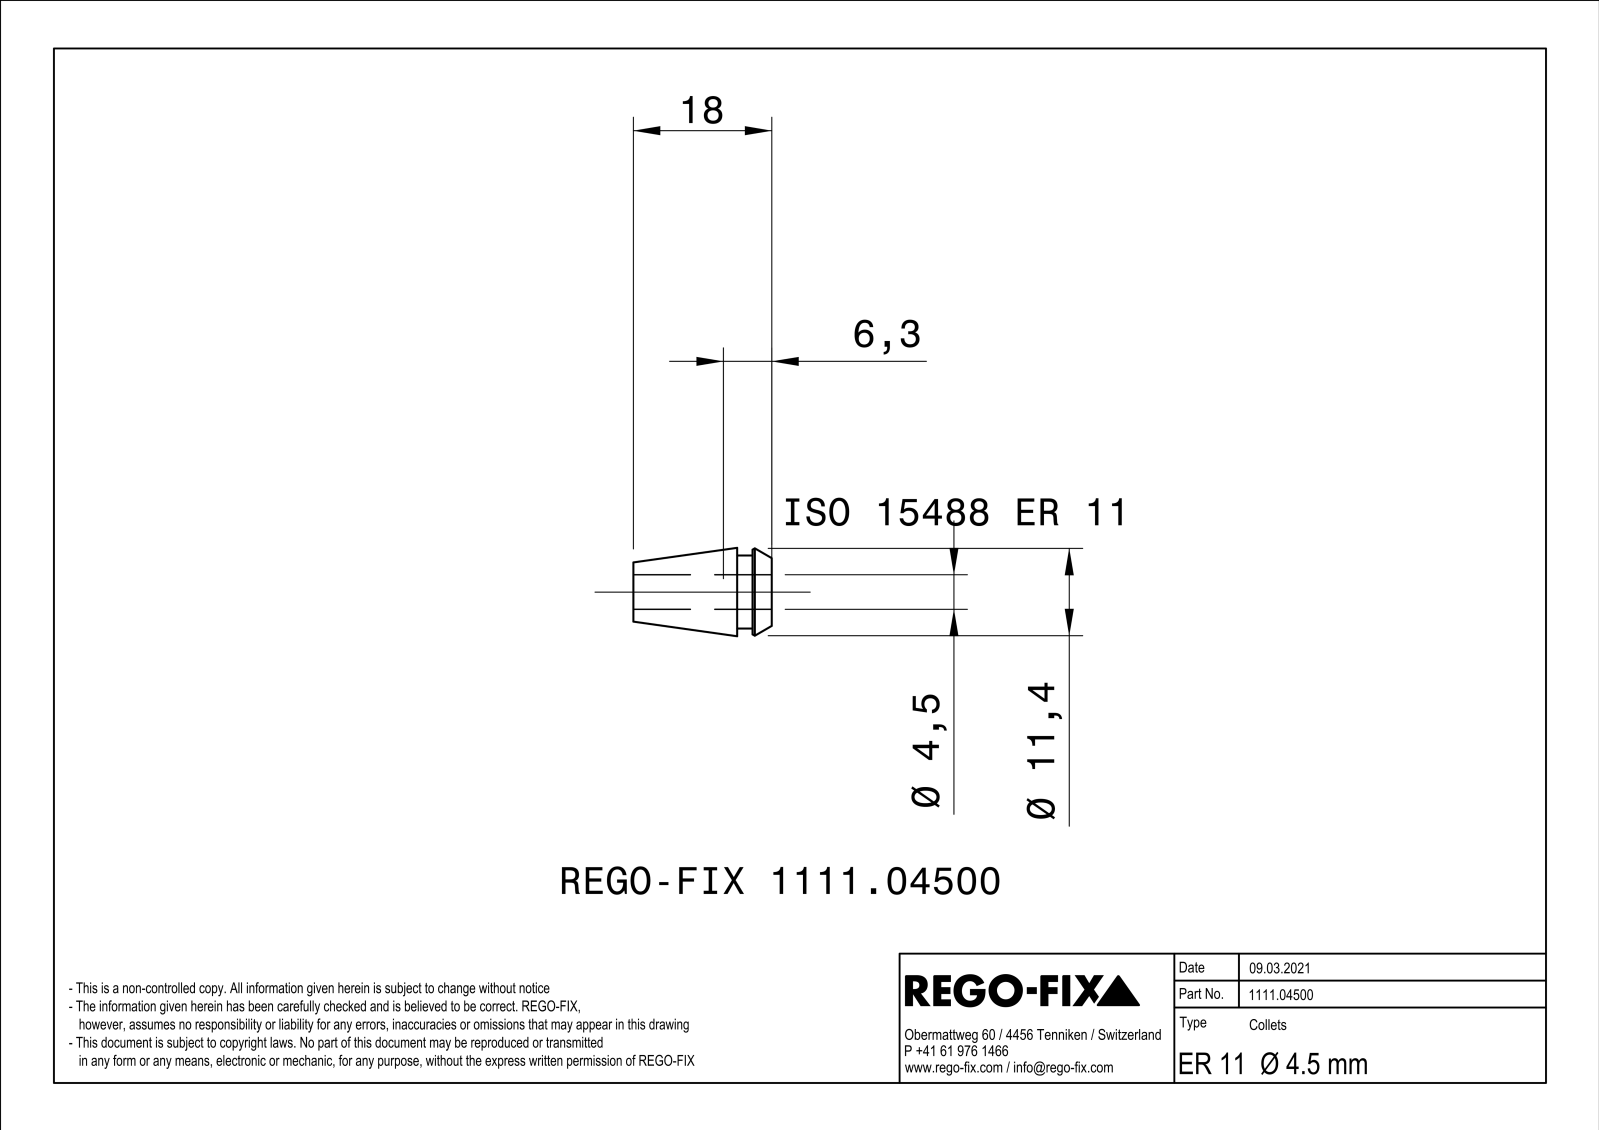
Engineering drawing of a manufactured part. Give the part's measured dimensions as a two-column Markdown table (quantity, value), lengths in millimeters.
| quantity | value |
| --- | --- |
| part name | NOCUT |
| STEP written by | SIEMENS PLM Software Solid Edge ST10 (AUTOMOTIVE_DESIGN) |
| units | millimeters |
| bodies | 1 solid, 157 faces (66 planar, 37 cylindrical, 54 other) |
| overall size | 18 × 11.5 × 11.49 |
| volume | 850 mm³ |
| surface area | 1 693 mm² |
| round holes (diameter × count) | 4.5 × 1 |
| round bosses / shafts (diameter × count) | 11.5 × 1, 9.5 × 1 |
| partial cylindrical surfaces (radius × count) | 25 × 12 |
| main face-to-face distances | 0.45, 0.46, 0.44, 2.5, 4.5, 2, 18, 15.5, 13.5, 4 |
